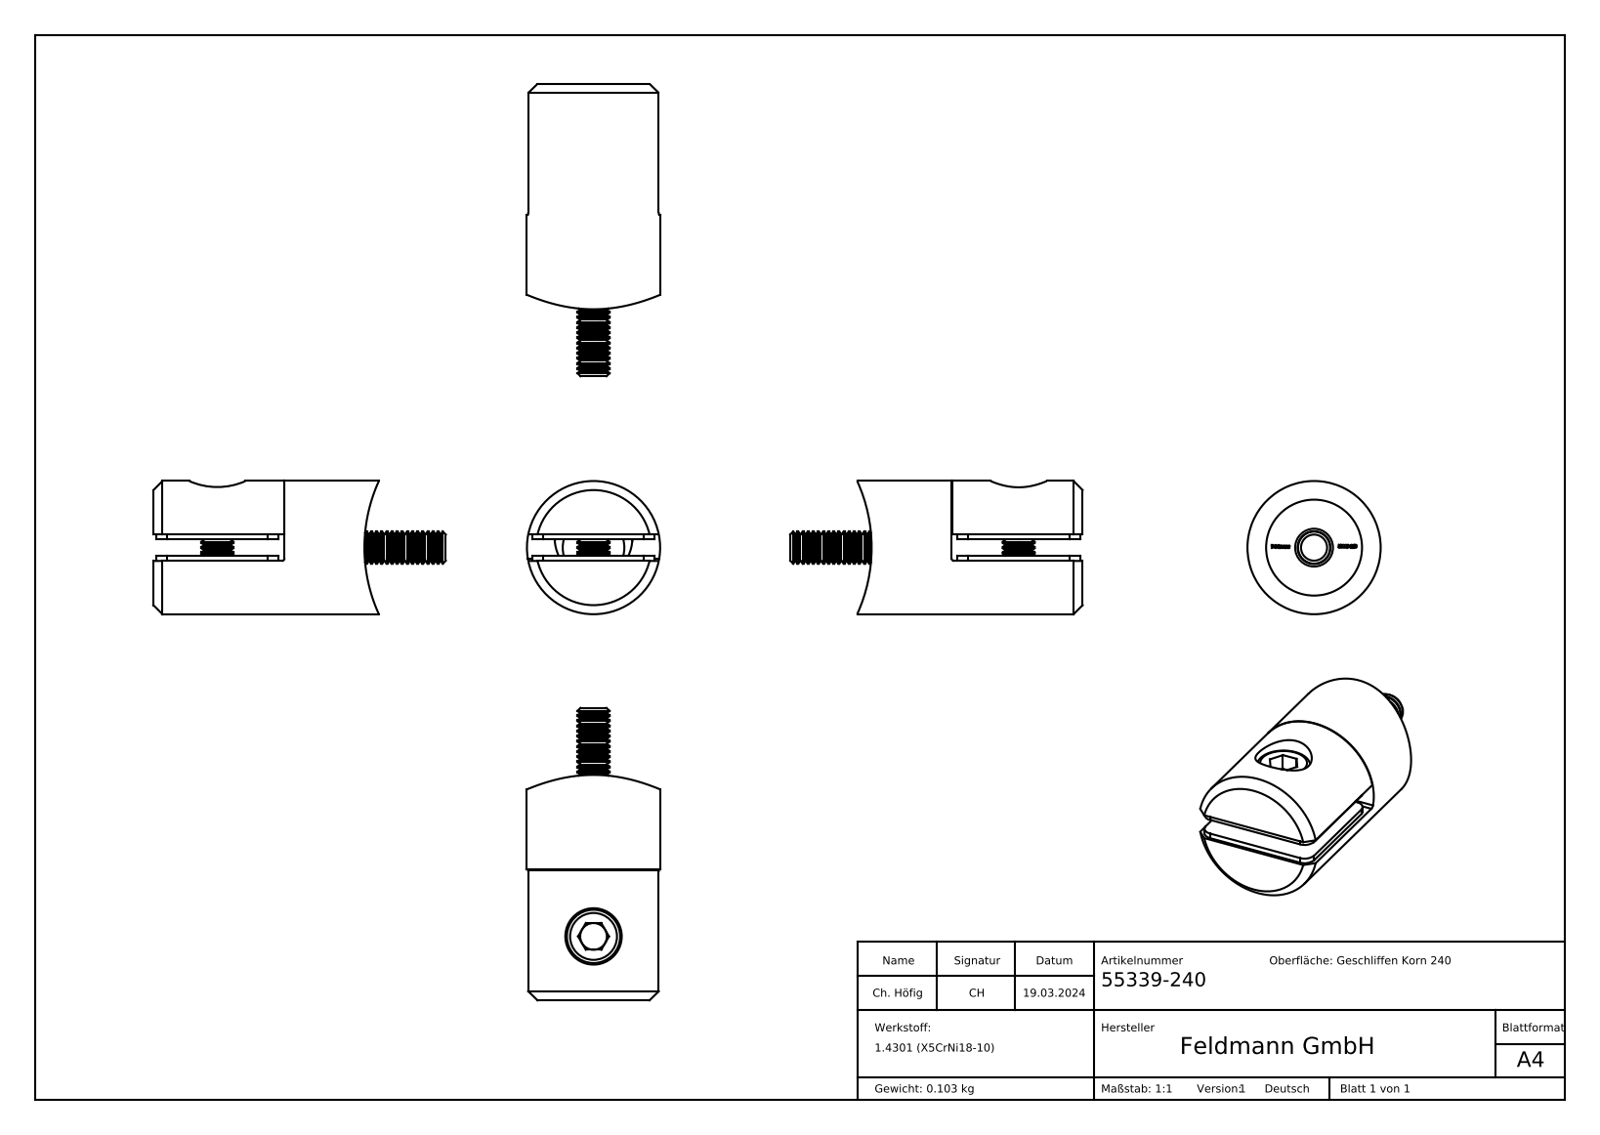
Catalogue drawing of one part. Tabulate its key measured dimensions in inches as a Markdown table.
| quantity | value |
| --- | --- |
| part name | socket countersunk head screw_din_DIN 7991 - M6 x 25 --- 25S; 5533X-240 Teil2_5533X-240 Teil2; 5533x-240 Teil3_5533x-240 Teil3; 5533X-240 Teil1_55339-240 Teil1 (+2 more) |
| STEP written by | SolidWorks 2018 (CONFIG_CONTROL_DESIGN) |
| units | inches |
| bodies | 6 solids, 715 faces (213 planar, 187 cylindrical, 315 other) |
| overall size | 2.161 × 0.984 × 0.984 |
| volume | 0.932 in³ |
| surface area | 16.27 in² |
| round holes (diameter × count) | 0.157 × 2, 0.226 × 1, 0.256 × 1, 0.276 × 1, 0.28 × 1, 0.417 × 1, 0.575 × 1, 0.709 × 1 |
| round bosses / shafts (diameter × count) | 0.236 × 2, 0.984 × 1, 0.456 × 1, 0.394 × 1 |
| partial cylindrical surfaces (radius × count) | 0.008 × 40, 0.079 × 6, 0.049 × 2, 0.02 × 1, 1.187 × 1 |
| main face-to-face distances | 0.157, 0.039, 0.197, 0.118, 1.358, 0.394, 0.965, 0.236, 0.39, 0.969 |
| hole center spacings | 0.369, 0.472 |
